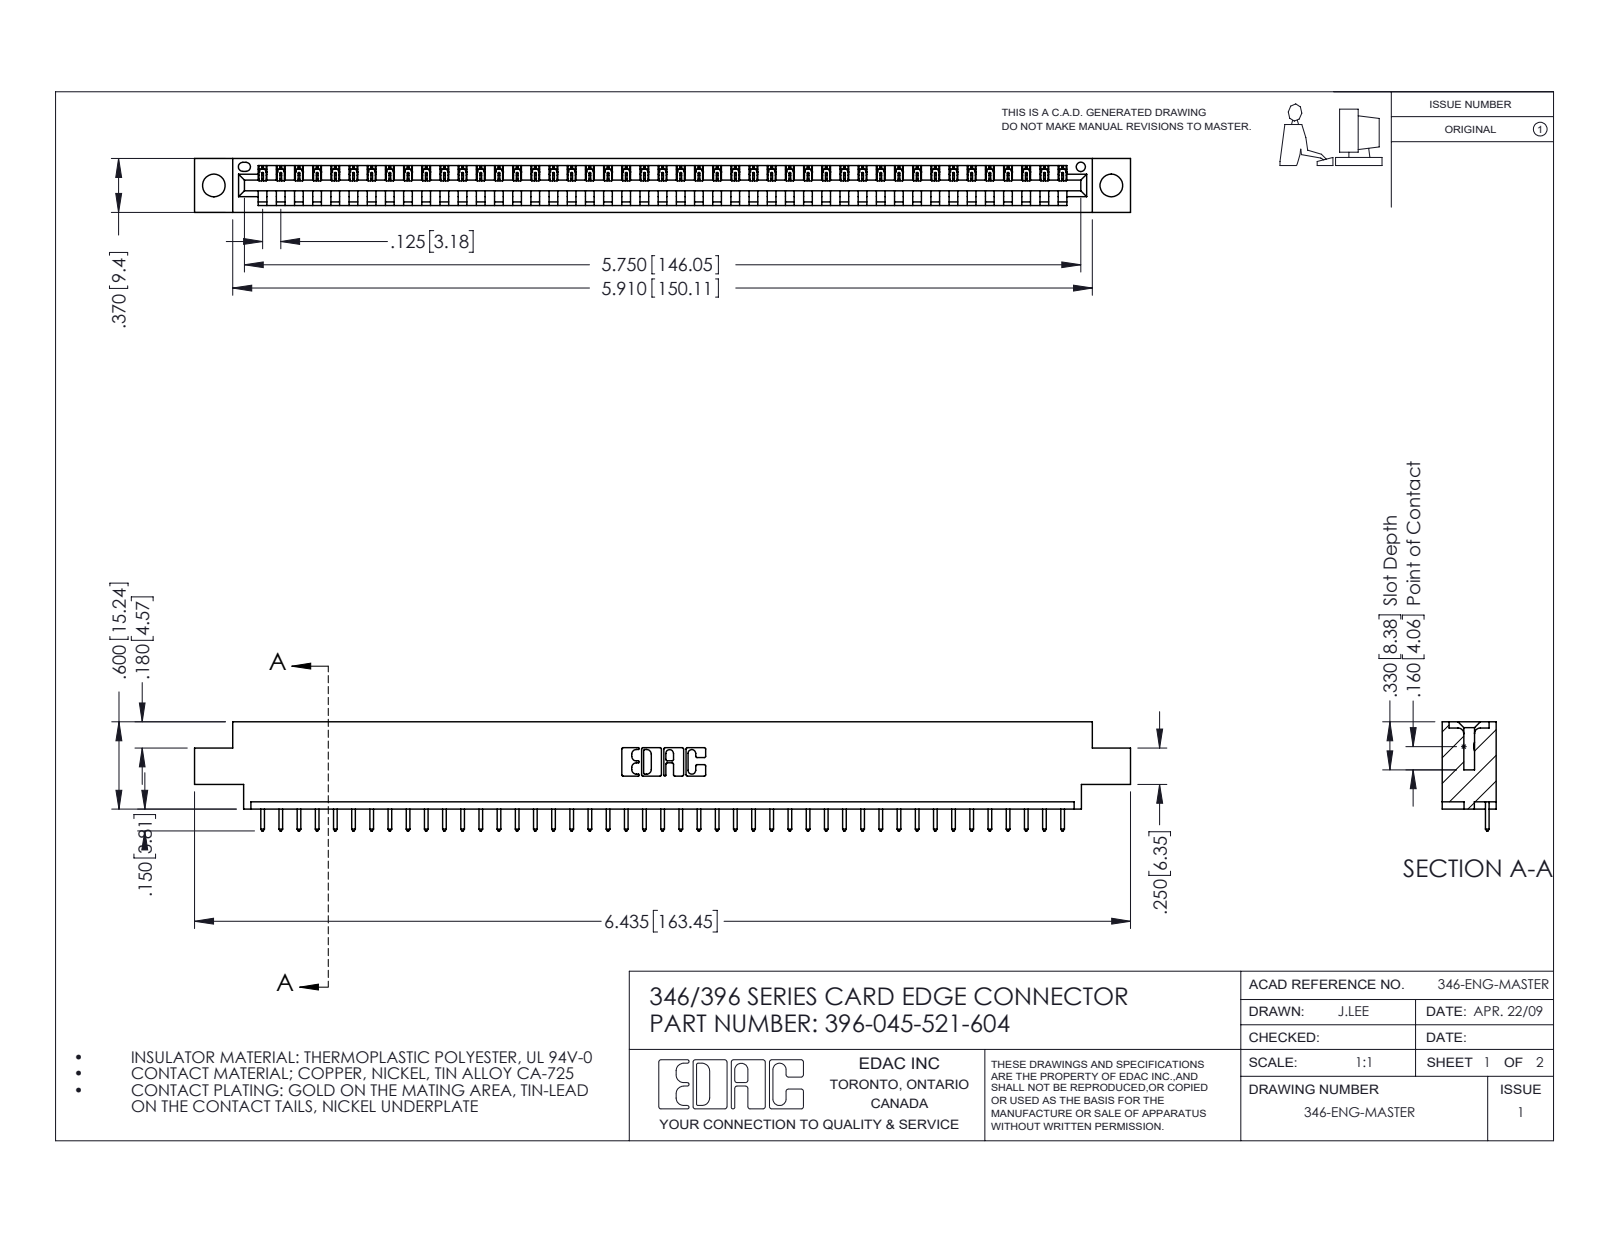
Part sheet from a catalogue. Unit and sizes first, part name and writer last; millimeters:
Units: millimetres
Overall size (bounding box): 163.4 × 19.1 × 9.4
Round holes (diameter × count): ⌀4 ×2, ⌀1.6 ×1
Partial cylindrical surfaces — rounded edges, fillets, slot ends (radius × count): R0.2 ×90, R0.3 ×90, R0.3 ×22, R0.2 ×6, R0.8 ×6, R0.7 ×3, R0.8 ×2, R1 ×2
Main face-to-face distances: 1.2, 8.2, 9.4, 6.4, 1.8, 7.6, 0.6, 3.8, 5.6, 2.5
Hole centre spacings: 6.2, 151.4, 156.7
Volume: 15 300 mm³ · Surface area: 18 610 mm²
Bodies: 46 solids, 2736 faces (1880 planar, 856 cylindrical, 0 other)
Part name (STEP PRODUCT): 396-045-521-604; 345-292-001_345-293-121; 346 Part_0.170 Offset - 0.156 Dia-TH
STEP written by: SolidWorks 2016 (CONFIG_CONTROL_DESIGN)
